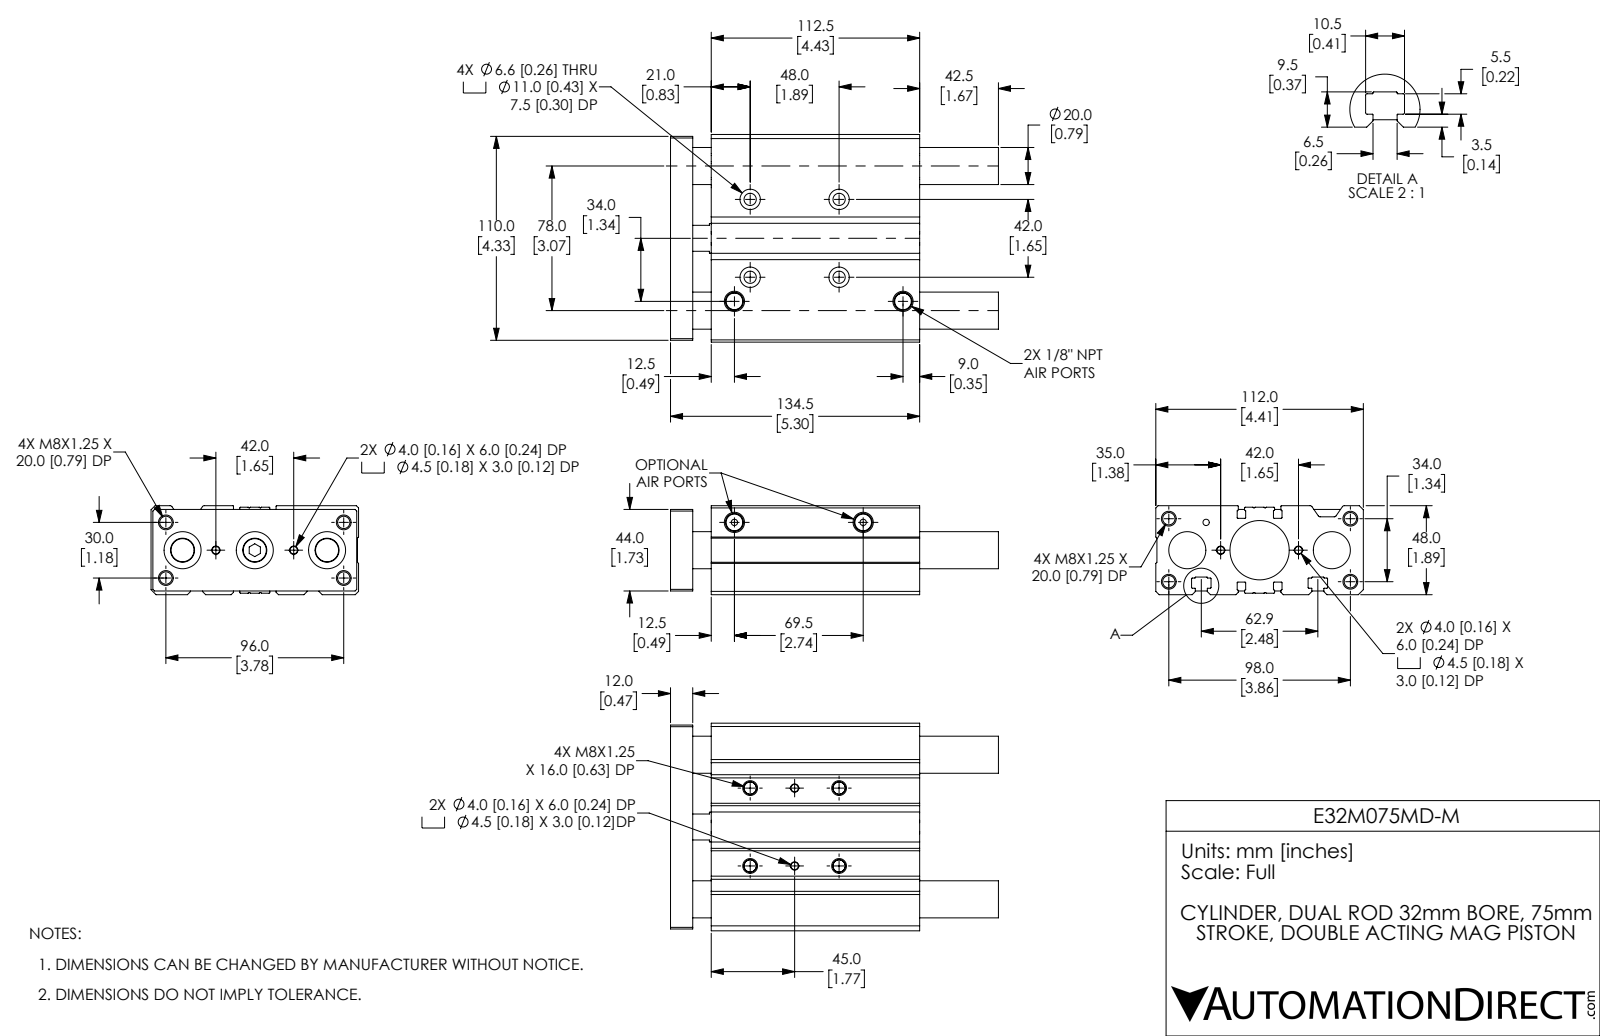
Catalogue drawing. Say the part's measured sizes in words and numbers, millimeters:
The part is named "E32M075MD-M_BODY; E32M075MD-M_ENDPLATE; E32M075MD-M". Its 3-D file was written by "SolidWorks 2019 (CONFIG_CONTROL_DESIGN)". It is 5 solids with 423 faces: 139 planar, 190 cylindrical and 94 other. Overall it measures 177 by 112 by 48 millimeters. Its volume is 585 497 cubic millimeters and its surface area 138 570 square millimeters. Round holes: 12 of diameter 6.65, 4 of diameter 4, 4 of diameter 4.5, 4 of diameter 6.6, 4 of diameter 11, 3 of diameter 10, 3 of diameter 20, 2 of diameter 3.43, 2 of diameter 12.95, 1 of diameter 3.43, 1 of diameter 20, 1 of diameter 32. Round bosses or shafts: 1 of diameter 16, 1 of diameter 12.95. Partial cylindrical surfaces (rounded edges, fillets, slot ends): 32 of radius 0.2, 28 of radius 0.4, 4 of radius 1.2, 2 of radius 0.3. The main face-to-face distances are 48, 6, 22, 0.8, 12, 10, 134.5, 122.5, 112.5, 112. The hole center spacings are 2.24, 17.49, 19.72, 24, 30.89, 32.02, 32.76, 42.
